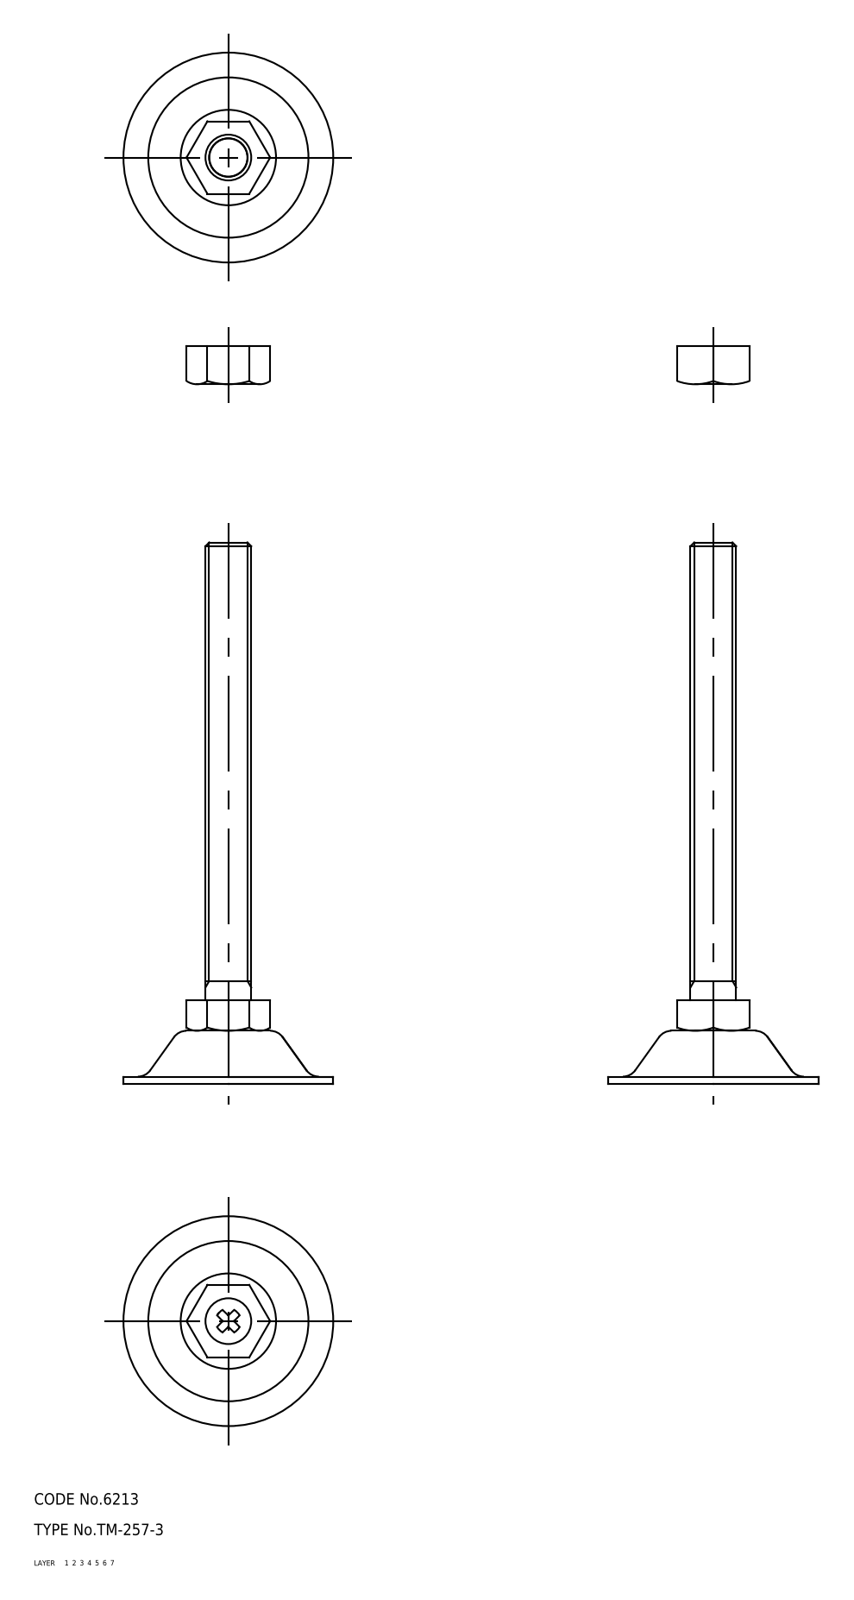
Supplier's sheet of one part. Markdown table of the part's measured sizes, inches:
| quantity | value |
| --- | --- |
| part name | nut; foot; bolt; TM_257_3_9773_36 |
| STEP written by | CADfix (AUTOMOTIVE_DESIGN) |
| units | inches |
| bodies | 4 solids, 95 faces (0 planar, 0 cylindrical, 95 other) |
| overall size | 5.591 × 2.165 × 2.165 |
| volume | 1.654 in³ |
| surface area | 23.42 in² |
